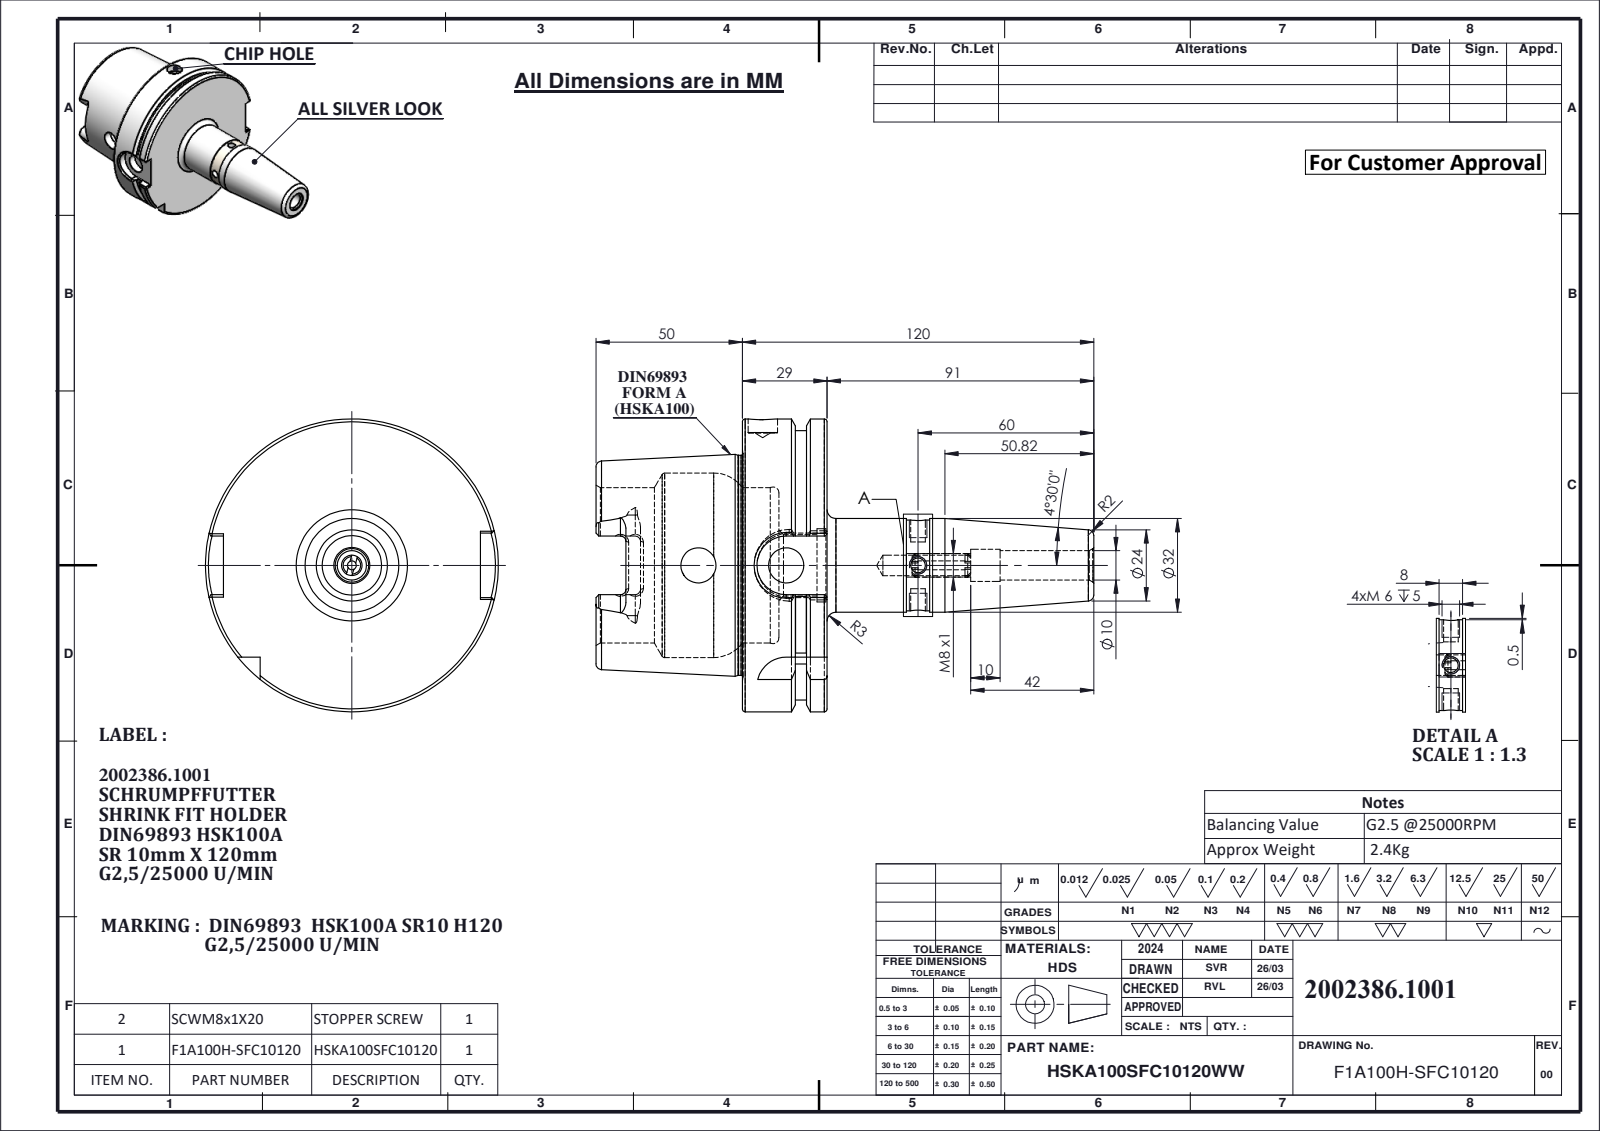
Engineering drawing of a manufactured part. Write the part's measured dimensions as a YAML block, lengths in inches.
part_name: "HSKA63SFC10120; F1A100H-SFC10120; SCWM8X1"
step_written_by: "SolidWorks 2024 (CONFIG_CONTROL_DESIGN)"
units: inches
bodies: {solids: 2, faces: 221, planar: 75, cylindrical: 68, other: 78}
overall_size: [6.693, 3.937, 3.937]
volume: 19.09
surface_area: 94.88
round_holes:
  - {diameter: 0.197, count: 2}
  - {diameter: 0.472, count: 2}
  - {diameter: 0.118, count: 1}
  - {diameter: 0.276, count: 1}
  - {diameter: 0.393, count: 1}
  - {diameter: 0.394, count: 1}
  - {diameter: 0.432, count: 1}
  - {diameter: 0.827, count: 1}
  - {diameter: 0.984, count: 1}
  - {diameter: 2.087, count: 1}
  - {diameter: 2.48, count: 1}
round_bosses_or_shafts:
  - {diameter: 3.937, count: 1}
  - {diameter: 3.622, count: 1}
  - {diameter: 2.959, count: 1}
  - {diameter: 1.26, count: 1}
  - {diameter: 1.22, count: 1}
  - {diameter: 0.315, count: 1}
partial_cylinders:
  - {radius: 0.071, count: 6}
  - {radius: 0.192, count: 4}
  - {radius: 0.394, count: 2}
  - {radius: 0.433, count: 1}
face_to_face_distances: [1.14, 0.492, 0.648, 2.461, 1.969, 3.108, 0.63, 3.091, 1.122, 0.018]
hole_center_spacings: [1.181, 1.772, 2.087, 2.953]
